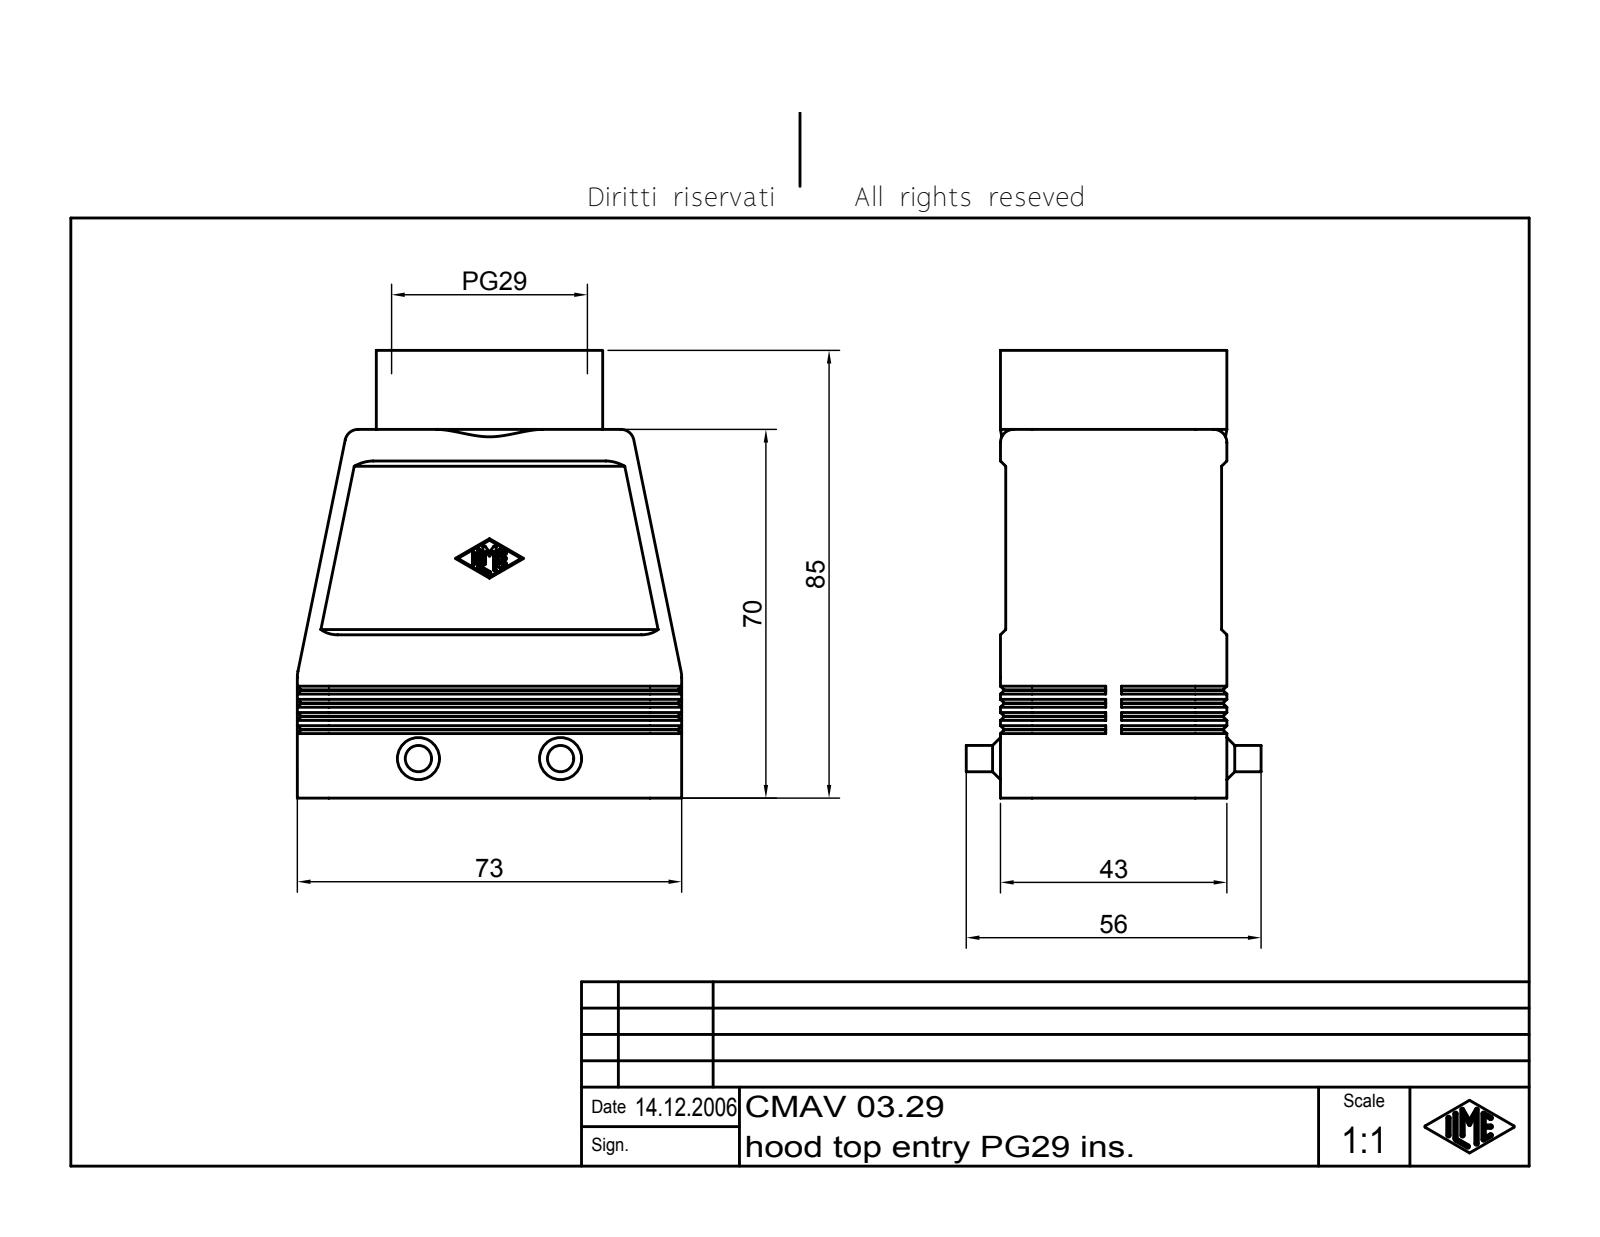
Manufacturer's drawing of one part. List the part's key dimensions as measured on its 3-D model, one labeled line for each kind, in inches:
Part name (STEP PRODUCT): CAO Tüllengehäuse 2 Bügel für einen Einsatz
STEP written by: Autodesk Inventor 7 (AUTOMOTIVE_DESIGN)
Units: inches
Bodies: 1 solid, 415 faces (153 planar, 108 cylindrical, 154 other)
Overall size (bounding box): 3.346 × 2.874 × 2.205
Volume: 3.595 in³ · Surface area: 56.46 in²
Round holes (diameter × count): ⌀1.318 ×1, ⌀1.397 ×1
Round bosses / shafts (diameter × count): ⌀0.197 ×2, ⌀1.693 ×1, ⌀1.357 ×1
Partial cylindrical surfaces — rounded edges, fillets, slot ends (radius × count): R0.01 ×14, R0.236 ×10, R0.079 ×4, R0.098 ×4, R0.118 ×4, R0.209 ×2
Main face-to-face distances: 0.118, 0.079, 0.039, 1.535, 1.457, 1.575, 1.654, 0.354, 0.472, 1.614
